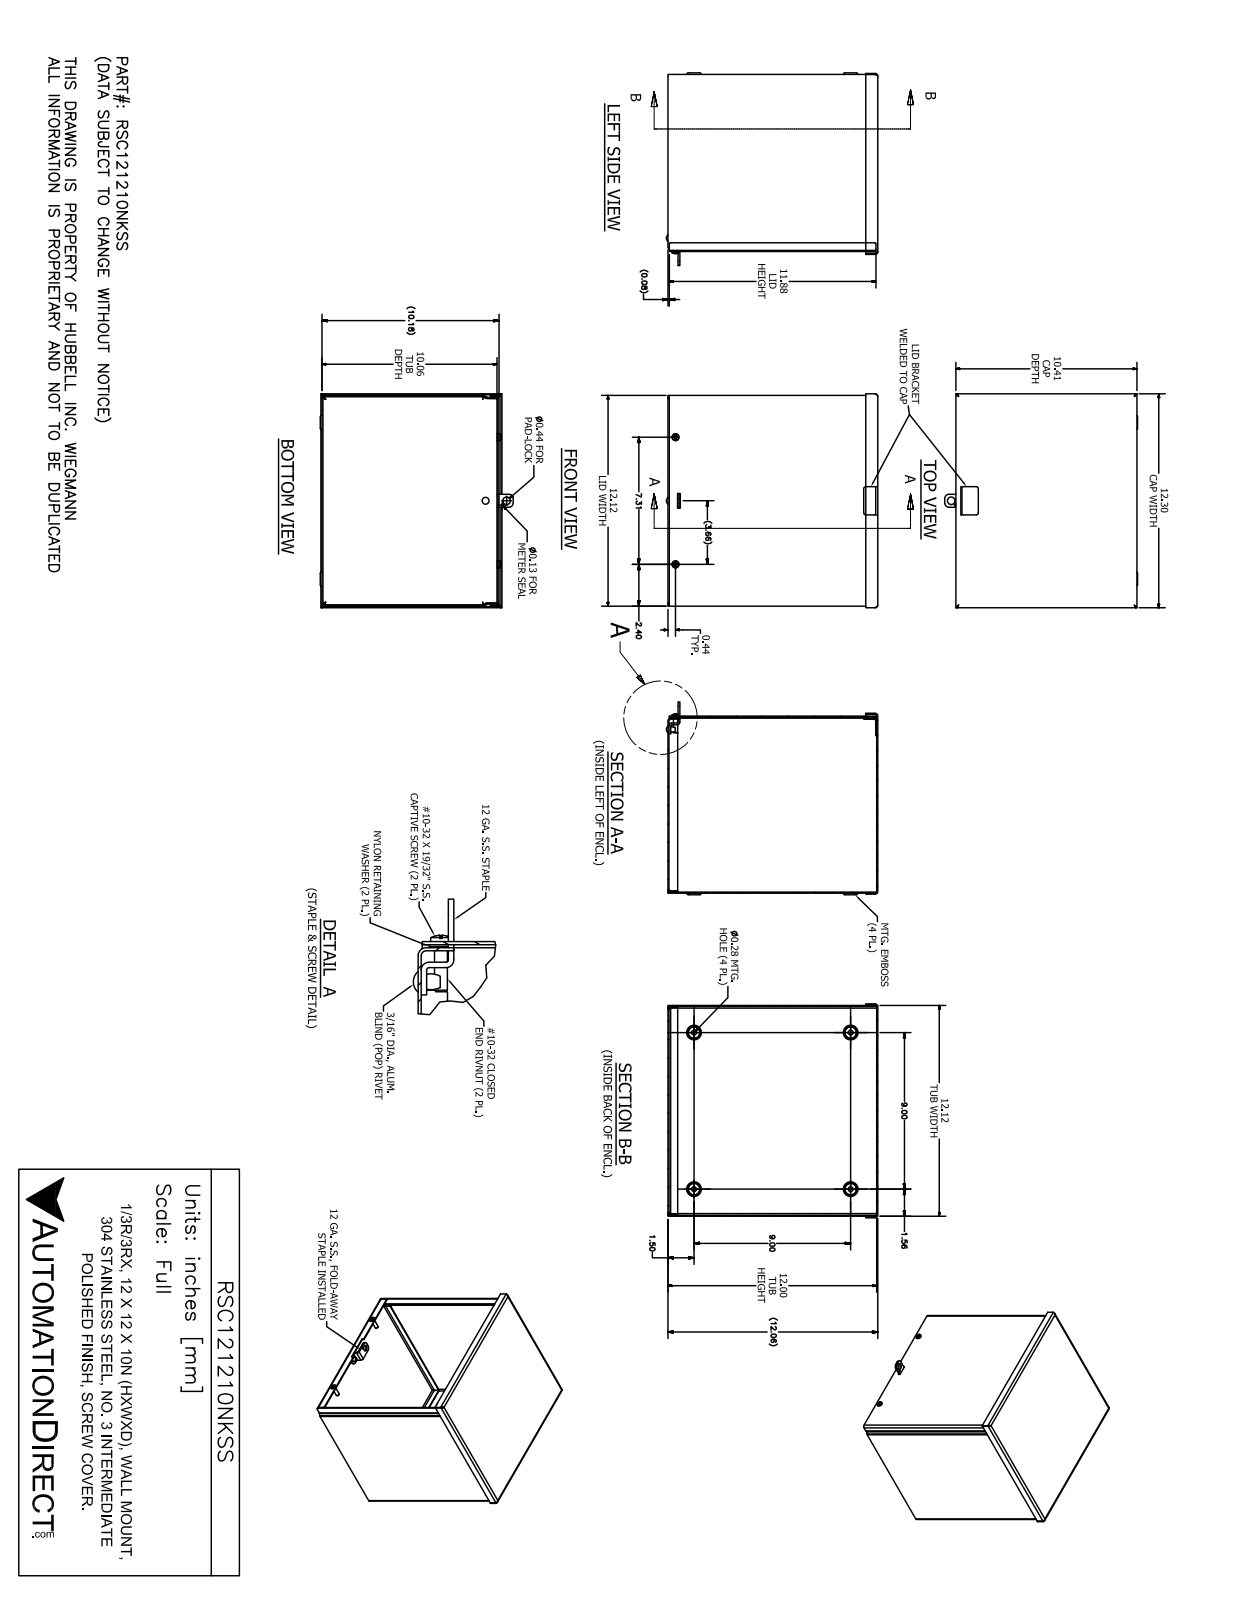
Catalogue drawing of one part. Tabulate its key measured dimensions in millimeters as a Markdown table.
| quantity | value |
| --- | --- |
| part name | RSC121210NKSS |
| STEP written by | SolidWorks 2017 (AUTOMOTIVE_DESIGN) |
| units | millimeters |
| bodies | 13 solids, 383 faces (199 planar, 99 cylindrical, 85 other) |
| overall size | 312.4 × 308.6 × 281.5 |
| volume | 811 000 mm³ |
| surface area | 1 092 000 mm² |
| round holes (diameter × count) | 6.4 × 4, 7.1 × 4, 4 × 2, 5 × 2, 6.5 × 2, 7.1 × 2, 3.2 × 1, 5 × 1, 5.1 × 1, 11.1 × 1 |
| round bosses / shafts (diameter × count) | 11.5 × 2, 10.3 × 2, 6.3 × 2, 4.2 × 2, 4.7 × 1 |
| partial cylindrical surfaces (radius × count) | 2.4 × 17, 3.9 × 17, 0.8 × 6, 3.2 × 4, 6.4 × 4, 1.2 × 2, 1.3 × 2, 1.6 × 2 |
| main face-to-face distances | 1.5, 306.3, 304.8, 257, 258.5, 255.5, 303.3, 307.8, 1.5, 3 |
| hole center spacings | 228.6, 34.5, 35.1, 185.8, 208.9, 209, 256.5, 257.3 |
